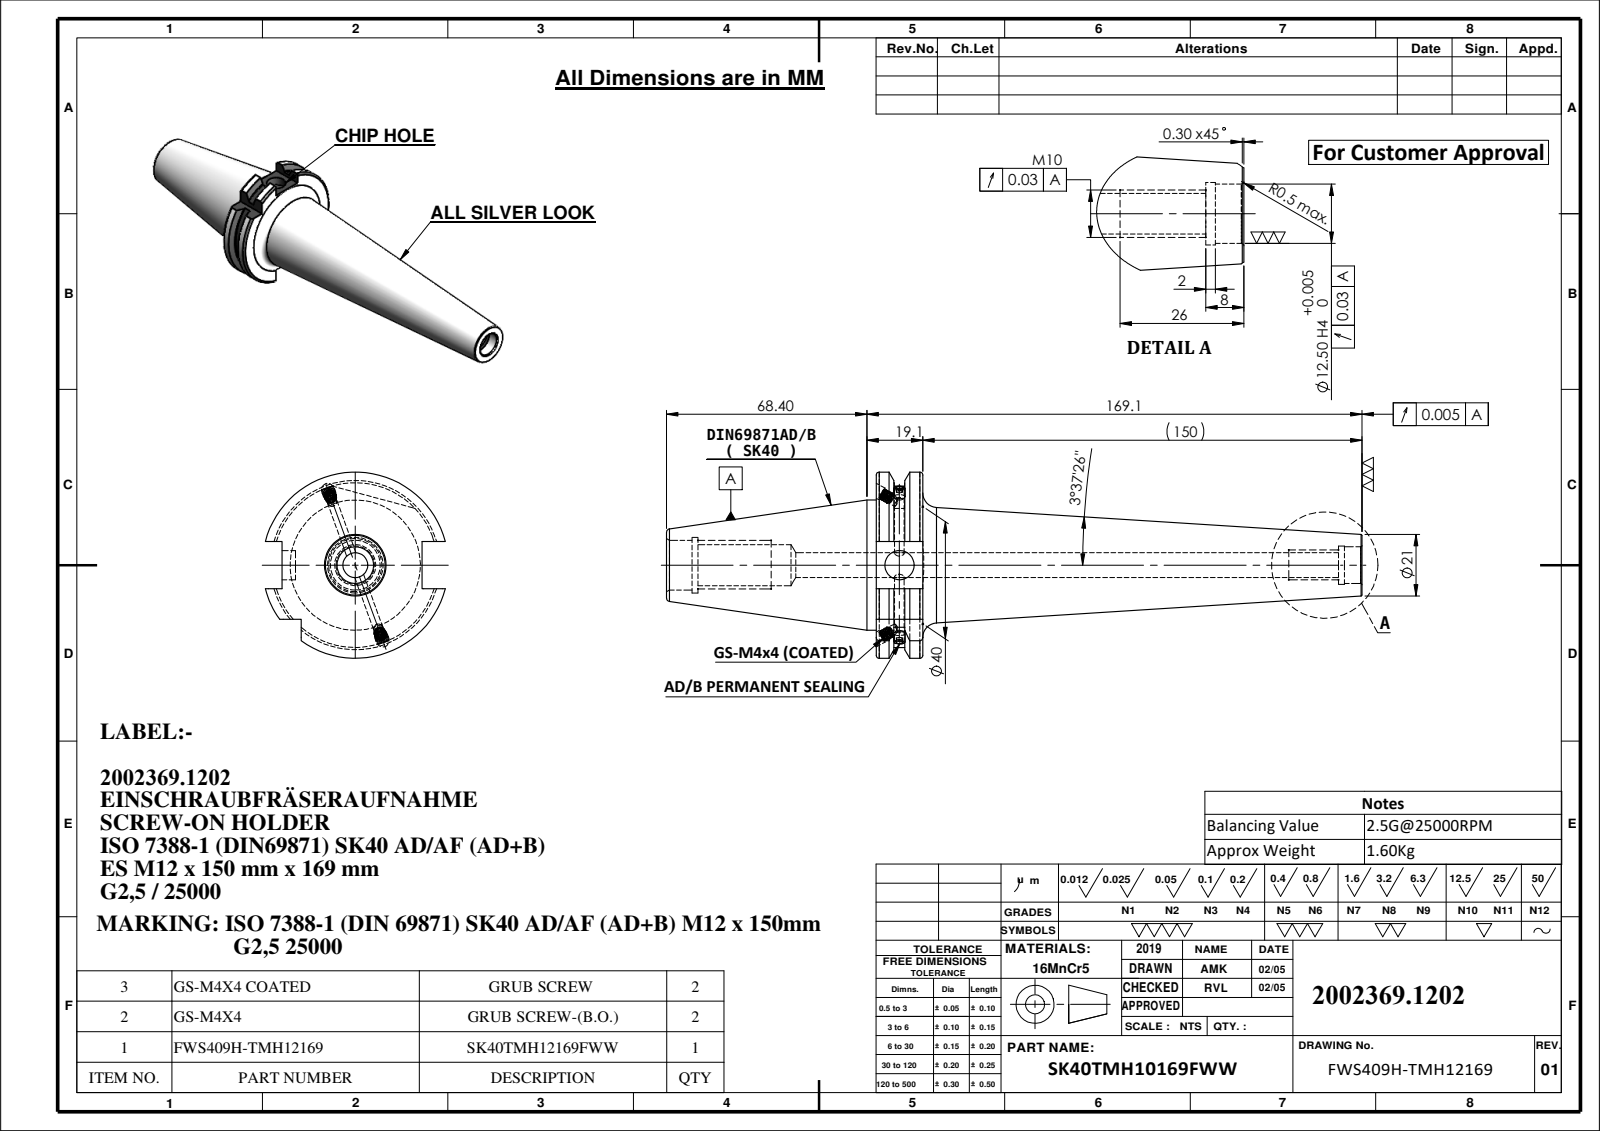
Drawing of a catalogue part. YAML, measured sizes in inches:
part_name: "GS-M4X4-COATING_DIN 913 - M4 x 4-N; SK40TMH12169FWW; FWS409H-TMH12169; M4X4_DIN 913 - M4 x 4-N"
step_written_by: "SolidWorks 2024 (CONFIG_CONTROL_DESIGN)"
units: inches
bodies: {solids: 5, faces: 238, planar: 64, cylindrical: 68, other: 106}
overall_size: [9.35, 2.502, 2.42]
volume: 12.66
surface_area: 59.57
round_holes:
  - {diameter: 0.13, count: 3}
  - {diameter: 0.177, count: 2}
  - {diameter: 0.335, count: 1}
  - {diameter: 0.394, count: 1}
  - {diameter: 0.492, count: 1}
  - {diameter: 0.516, count: 1}
  - {diameter: 0.551, count: 1}
  - {diameter: 0.669, count: 1}
  - {diameter: 0.748, count: 1}
round_bosses_or_shafts:
  - {diameter: 0.157, count: 4}
  - {diameter: 0.114, count: 2}
  - {diameter: 1.75, count: 1}
partial_cylinders:
  - {radius: 1.107, count: 1}
  - {radius: 1.251, count: 1}
face_to_face_distances: [0.626, 6.531, 5.906, 0.634, 1.882, 2.819, 3.445, 9.35, 0.421, 2.398]
